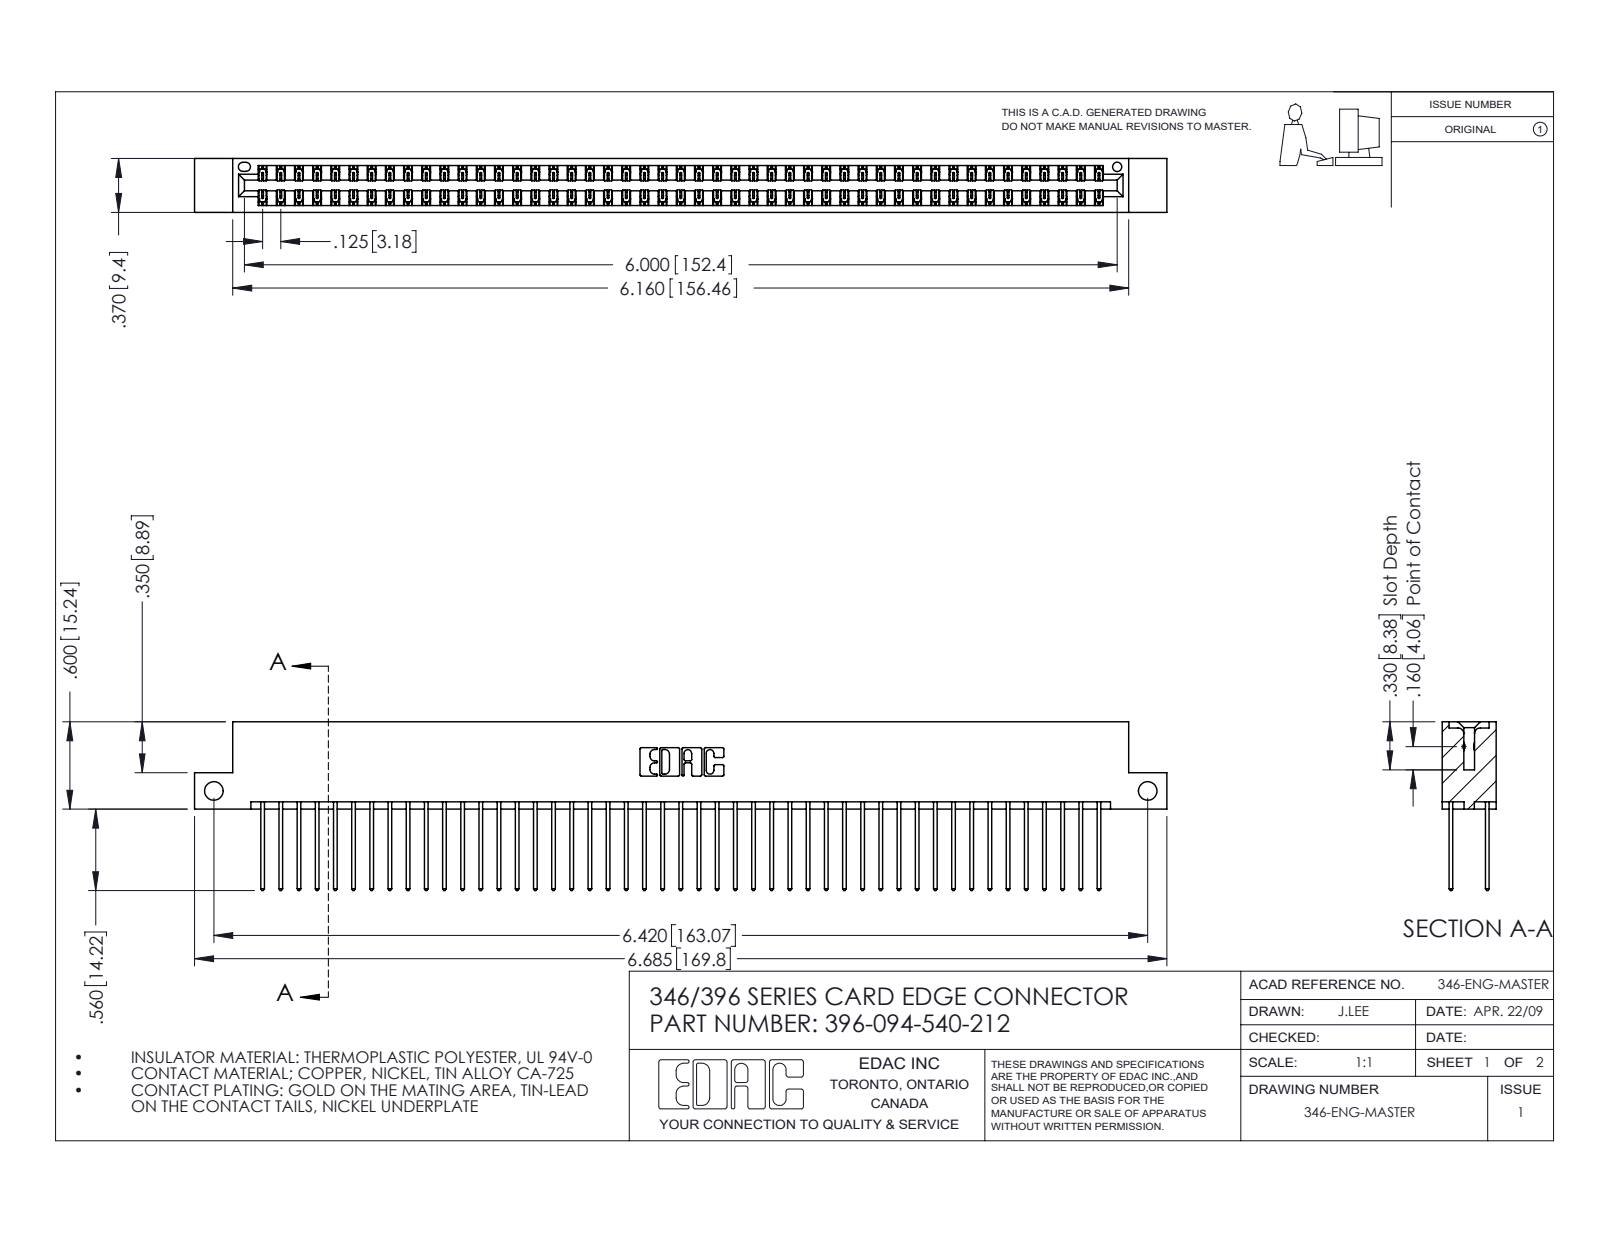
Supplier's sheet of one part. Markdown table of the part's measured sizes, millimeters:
| quantity | value |
| --- | --- |
| part name | 346 Part_Flush Mounting Lugs - Side Mount; 345-292-001_345-293-140; 396-094-540-212 |
| STEP written by | SolidWorks 2016 (CONFIG_CONTROL_DESIGN) |
| units | millimeters |
| bodies | 95 solids, 5010 faces (3366 planar, 1644 cylindrical, 0 other) |
| overall size | 169.8 × 29.5 × 9.4 |
| volume | 16 860 mm³ |
| surface area | 24 810 mm² |
| round holes (diameter × count) | 3.3 × 2, 1.6 × 1 |
| partial cylindrical surfaces (radius × count) | 0.2 × 141, 0.3 × 94, 0.3 × 22, 0.2 × 6, 0.8 × 6, 0.7 × 3, 0.4 × 2, 0.6 × 2 |
| main face-to-face distances | 1.2, 8.2, 6.4, 1.8, 7.6, 0.6, 9.4, 7, 3.8, 5.6 |
| hole center spacings | 163.1 |
